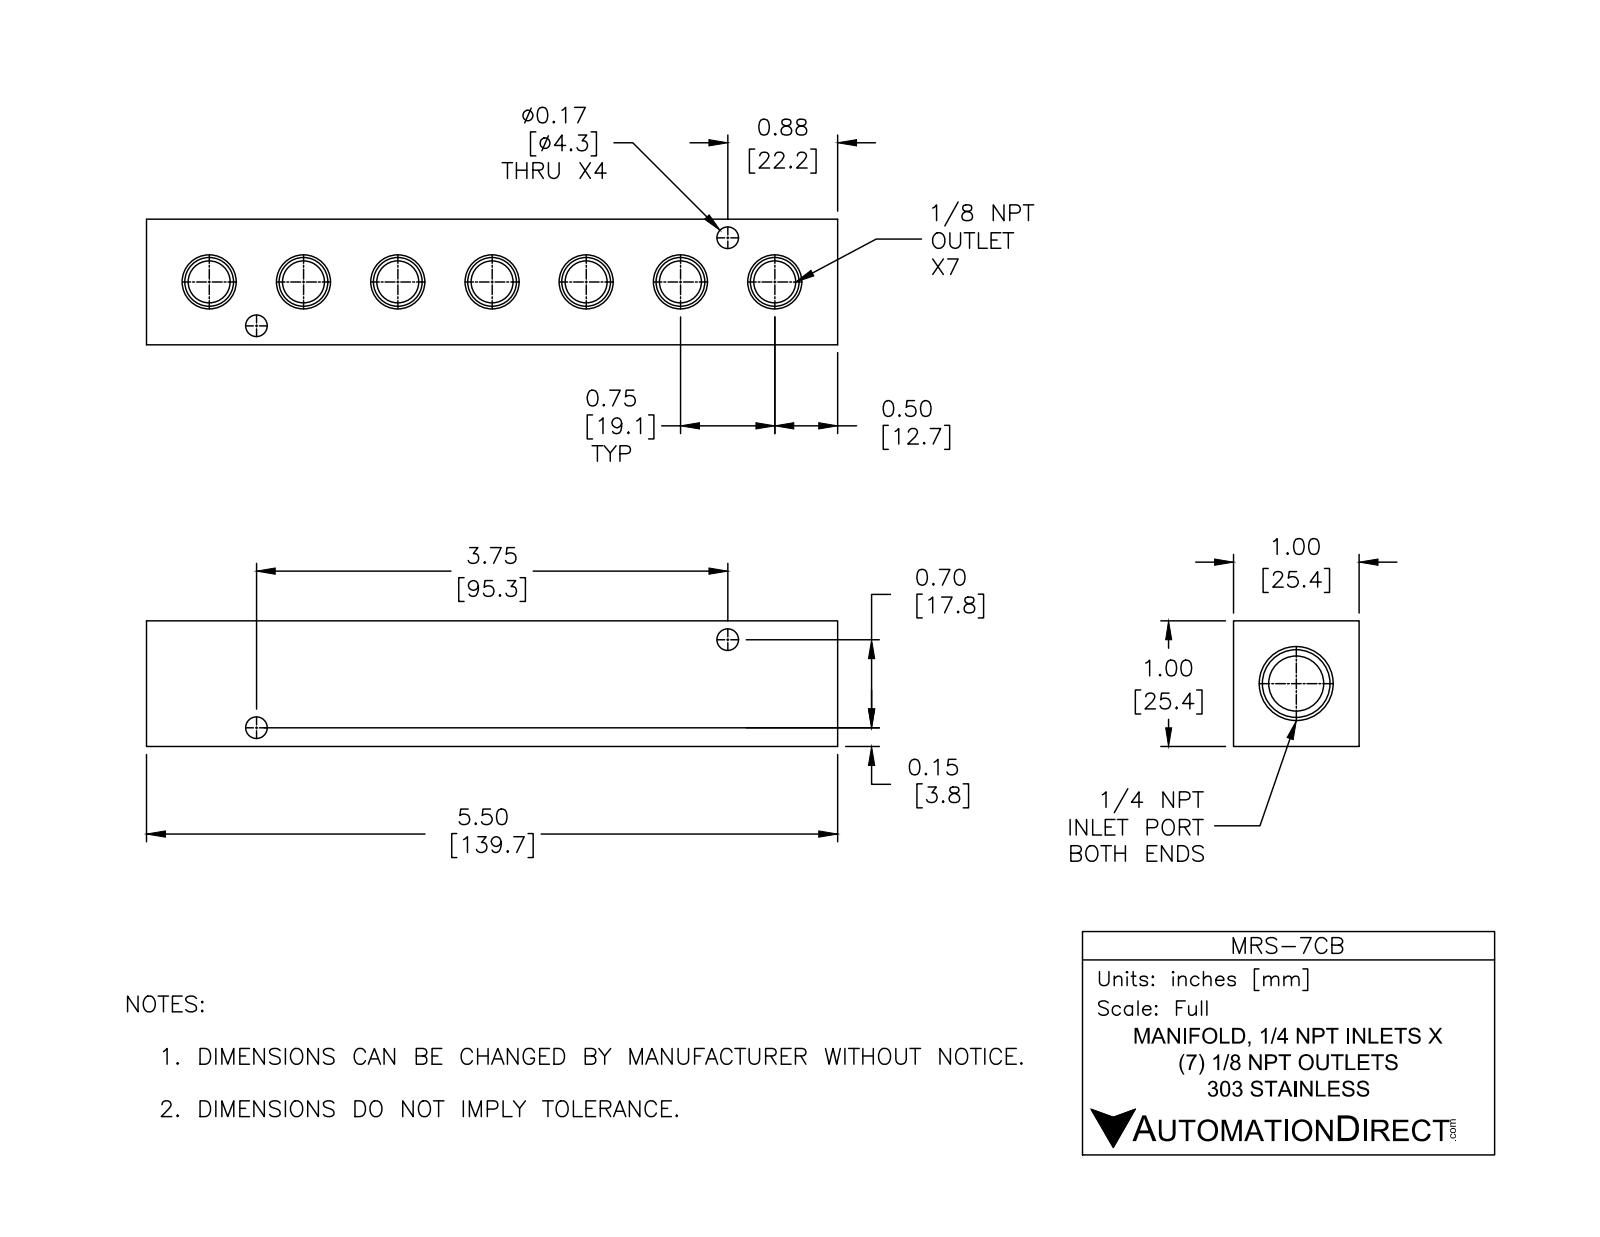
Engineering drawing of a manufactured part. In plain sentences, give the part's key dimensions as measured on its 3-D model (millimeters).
The part is named "MRS-7CB". Its 3-D file was written by "SolidWorks 2015 (CONFIG_CONTROL_DESIGN)". It is 1 solid with 82 faces: 15 planar, 31 cylindrical and 36 other. Overall it measures 139.7 by 25.4 by 25.4 millimeters. Its volume is 70 140 cubic millimeters and its surface area 22 170 square millimeters. Round holes: 5 of diameter 8.4, 4 of diameter 4.3, 1 of diameter 11.1. Partial cylindrical surfaces (rounded edges, fillets, slot ends): 2 of radius 4.2. The main face-to-face distances are 25.4, 139.7, 18.5, 6.9, 9.9, 129.8, 119.9. The hole center spacings are 19.1, 38.1, 13, 29.9, 48.4, 57.2, 67.3, 86.2.
